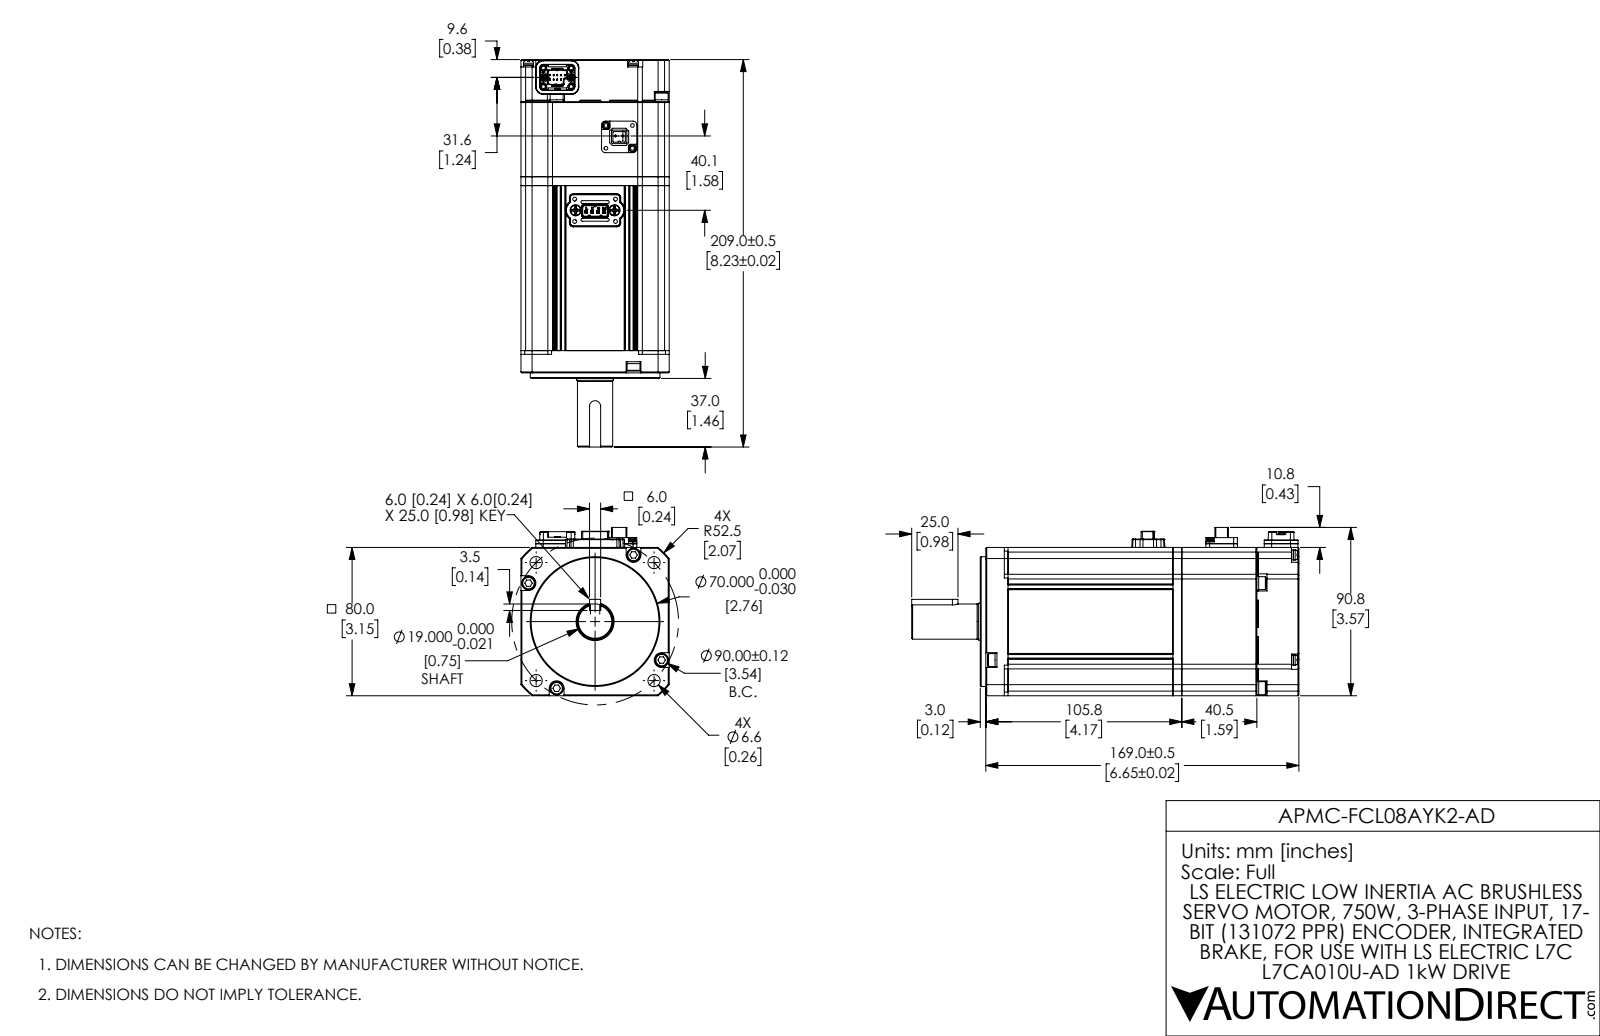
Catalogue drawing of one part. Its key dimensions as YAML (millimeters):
part_name: "APMC-FCL08AYK2-AD"
step_written_by: "SolidWorks 2017 (AUTOMOTIVE_DESIGN)"
units: millimeters
bodies: {solids: 50, faces: 2072, planar: 1317, cylindrical: 552, other: 203}
overall_size: [209, 90.8, 80]
volume: 973100
surface_area: 147000
round_holes:
  - {diameter: 2.1, count: 10}
  - {diameter: 4, count: 8}
  - {diameter: 4.5, count: 8}
  - {diameter: 2, count: 6}
  - {diameter: 3, count: 6}
  - {diameter: 3.5, count: 4}
  - {diameter: 6.6, count: 4}
  - {diameter: 1, count: 2}
  - {diameter: 6, count: 2}
  - {diameter: 3.3, count: 1}
  - {diameter: 3.4, count: 1}
  - {diameter: 13, count: 1}
round_bosses_or_shafts:
  - {diameter: 7.2, count: 8}
  - {diameter: 7, count: 8}
  - {diameter: 5.4, count: 6}
  - {diameter: 4.2, count: 2}
  - {diameter: 3.6, count: 2}
  - {diameter: 3.5, count: 2}
  - {diameter: 2.2, count: 2}
  - {diameter: 0.9, count: 2}
partial_cylinders:
  - {radius: 0.3, count: 36}
  - {radius: 0.2, count: 20}
  - {radius: 2, count: 12}
  - {radius: 1, count: 10}
  - {radius: 0.2, count: 9}
  - {radius: 2.5, count: 9}
  - {radius: 4, count: 9}
  - {radius: 0.5, count: 7}
face_to_face_distances: [80, 4.8, 46, 93.8, 89, 40.5, 45.3, 134.3, 0.7, 41.2]
hole_center_spacings: [41.5, 11.8, 52.7, 58.7, 68.7, 85.8, 5, 6]
